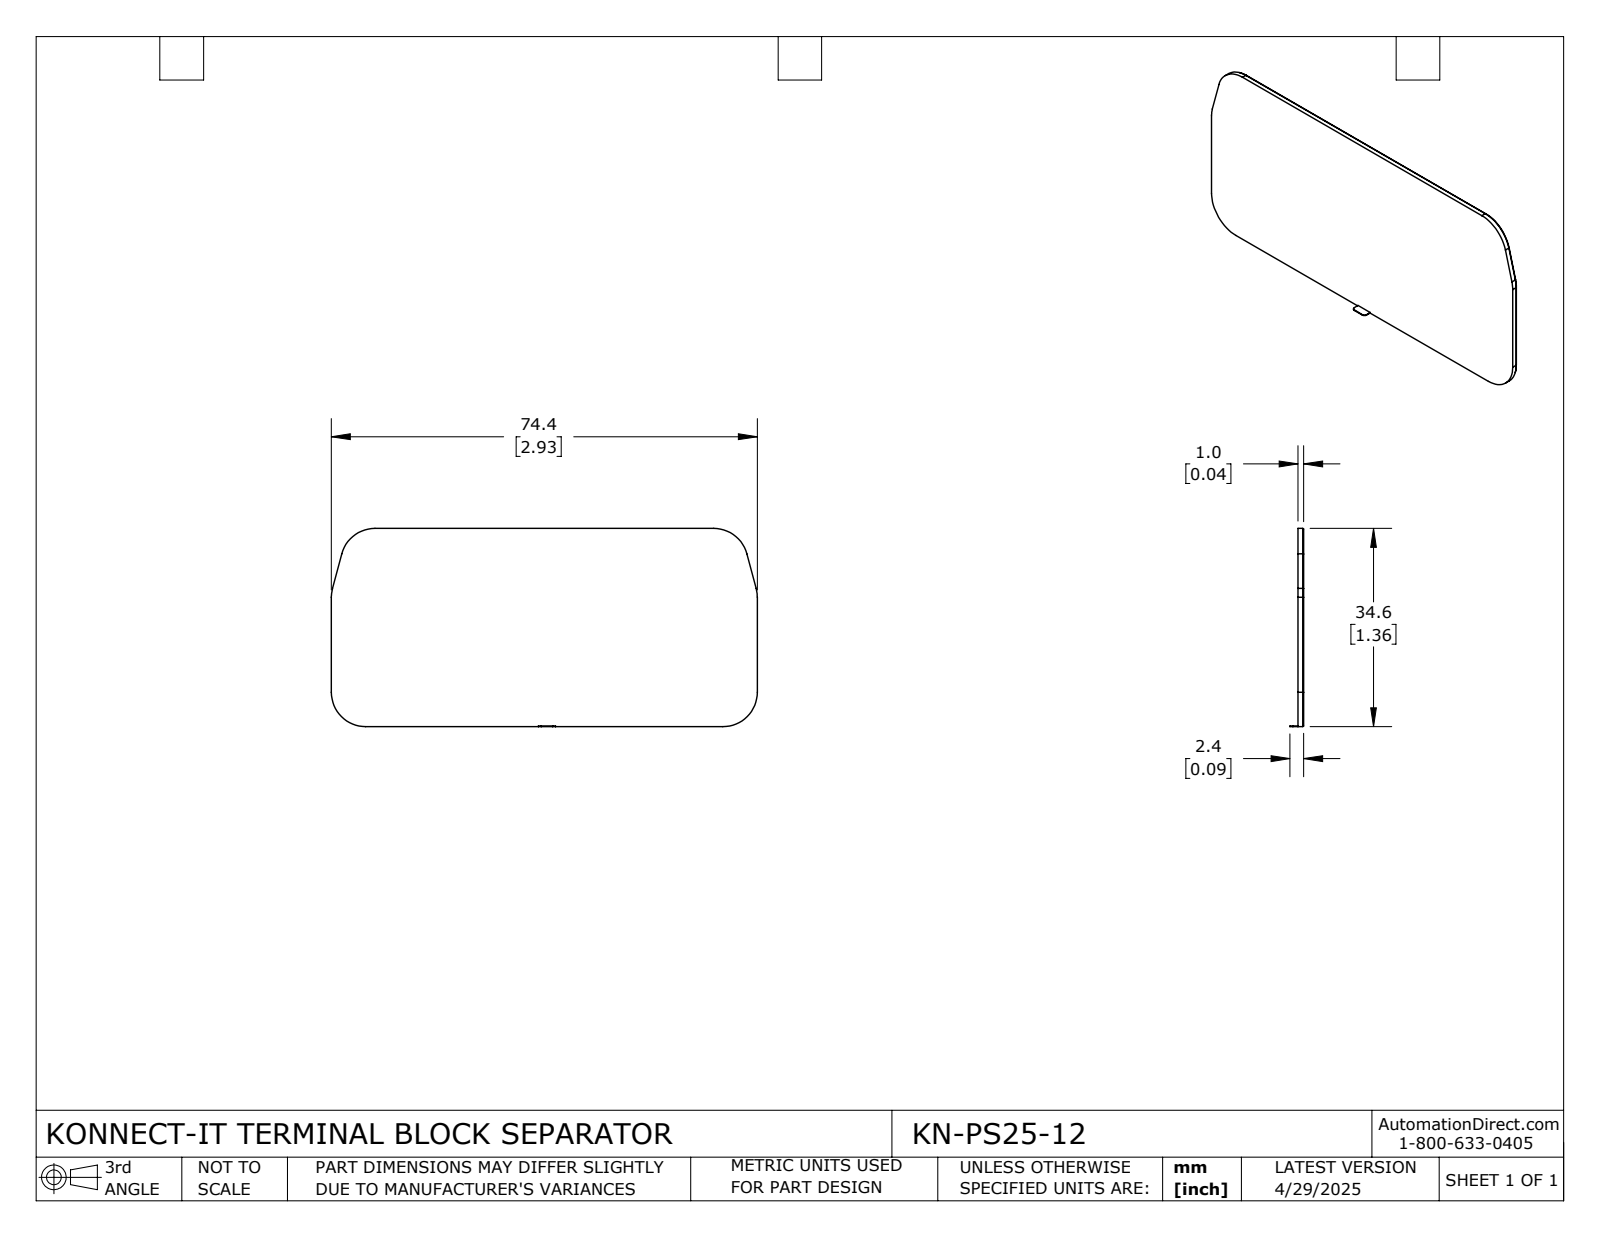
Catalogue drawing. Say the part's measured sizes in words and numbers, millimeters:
The part is named "KN-PS25-12". Its 3-D file was written by "SolidWorks 2024 (CONFIG_CONTROL_DESIGN)". It is 1 solid with 33 faces: 19 planar, 14 cylindrical and 0 other. Overall it measures 74.37 by 34.61 by 2.4 millimeters. Its volume is 2 514 cubic millimeters and its surface area 5 246 square millimeters. Partial cylindrical surfaces (rounded edges, fillets, slot ends): 6 of radius 5.9, 6 of radius 6, 2 of radius 0.5. The main face-to-face distances are 1, 34.61, 34.51, 0.85, 74.37, 34.41, 74.27, 74.17, 1.4, 2.25.
